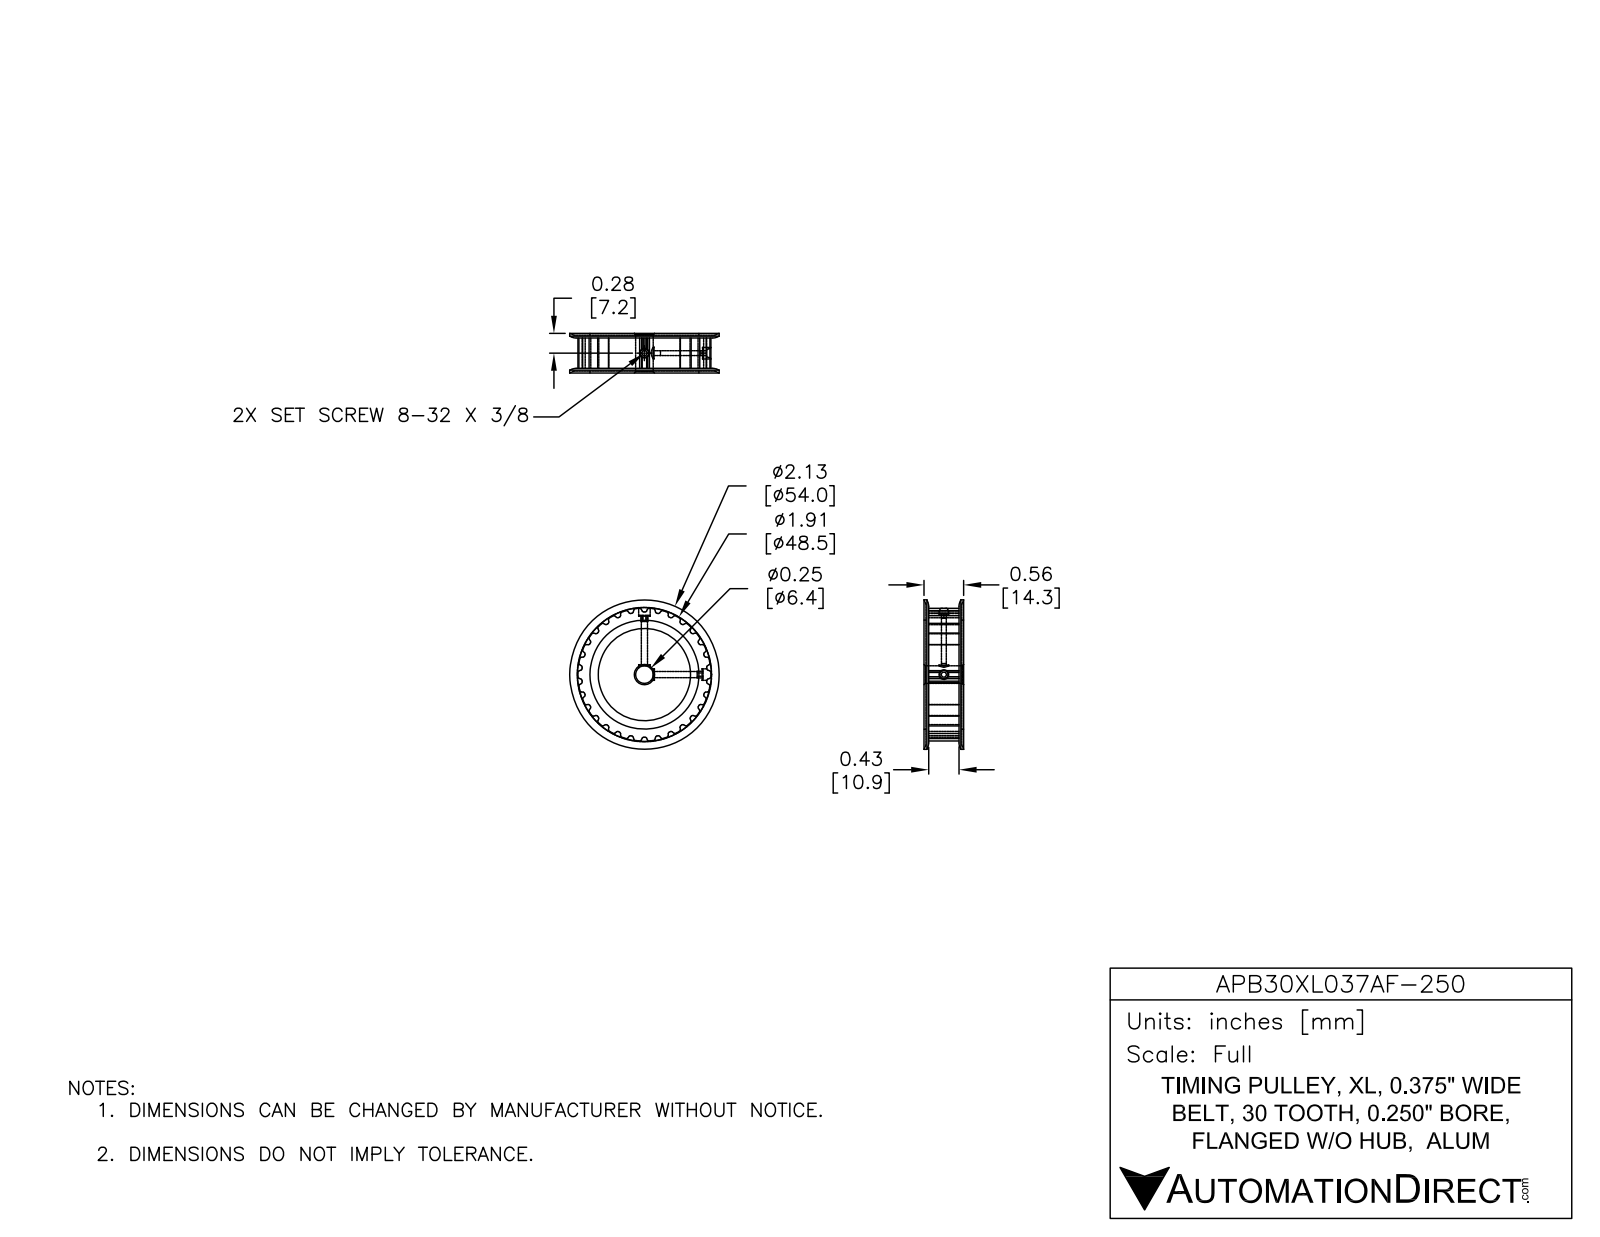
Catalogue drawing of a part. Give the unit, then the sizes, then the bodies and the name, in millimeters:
Units: millimetres
Overall size (bounding box): 54 × 54 × 14.2
Round holes (diameter × count): ⌀3.2 ×2, ⌀6.4 ×1
Round bosses / shafts (diameter × count): ⌀33.4 ×1
Partial cylindrical surfaces — rounded edges, fillets, slot ends (radius × count): R0.4 ×120, R22.6 ×1
Main face-to-face distances: 12.6, 0.8, 13.4, 14.1, 13.3, 0.8, 18, 48, 1.7, 0.8
Volume: 23 270 mm³ · Surface area: 8 832 mm²
Bodies: 1 solid, 312 faces (103 planar, 186 cylindrical, 23 other)
Part name (STEP PRODUCT): APB30XL037AF-250
STEP written by: SolidWorks 2014 (AUTOMOTIVE_DESIGN)
